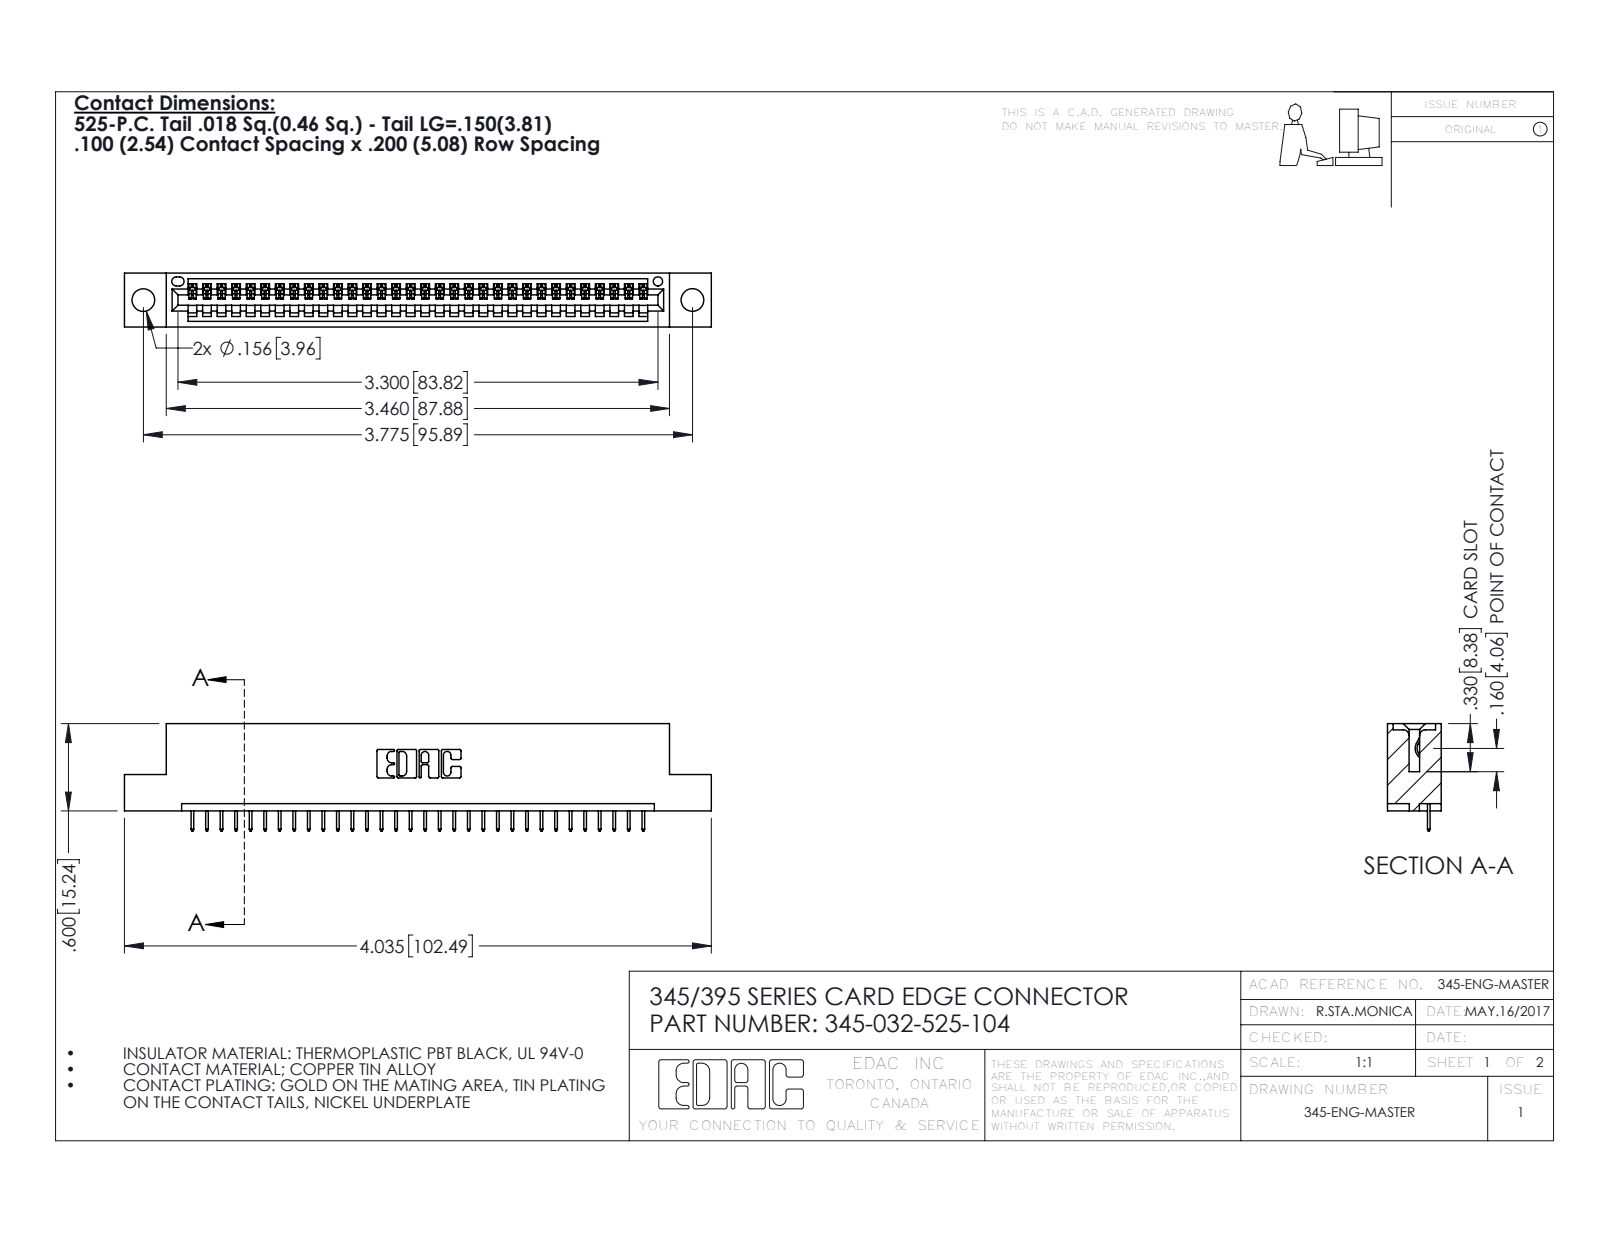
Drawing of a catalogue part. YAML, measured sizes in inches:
part_name: "345-292-001_345-293-125; 345 Part_Flush Mounting Lugs - 0.156 Dia-TH; 345-032-525-104"
step_written_by: "SolidWorks 2020 (CONFIG_CONTROL_DESIGN)"
units: inches
bodies: {solids: 33, faces: 2110, planar: 1552, cylindrical: 558, other: 0}
overall_size: [4.035, 0.737, 0.37]
volume: 0.576
surface_area: 18.25
round_holes:
  - {diameter: 0.156, count: 2}
  - {diameter: 0.064, count: 1}
partial_cylinders:
  - {radius: 0.006, count: 64}
  - {radius: 0.01, count: 22}
  - {radius: 0.007, count: 6}
  - {radius: 0.031, count: 6}
  - {radius: 0.026, count: 3}
  - {radius: 0.031, count: 2}
  - {radius: 0.04, count: 2}
  - {radius: 0.014, count: 1}
face_to_face_distances: [0.298, 0.072, 0.37, 0.2, 0.098, 0.272, 0.025, 0.225, 0.072, 0.149]
hole_center_spacings: [0.27, 3.54, 3.775]
